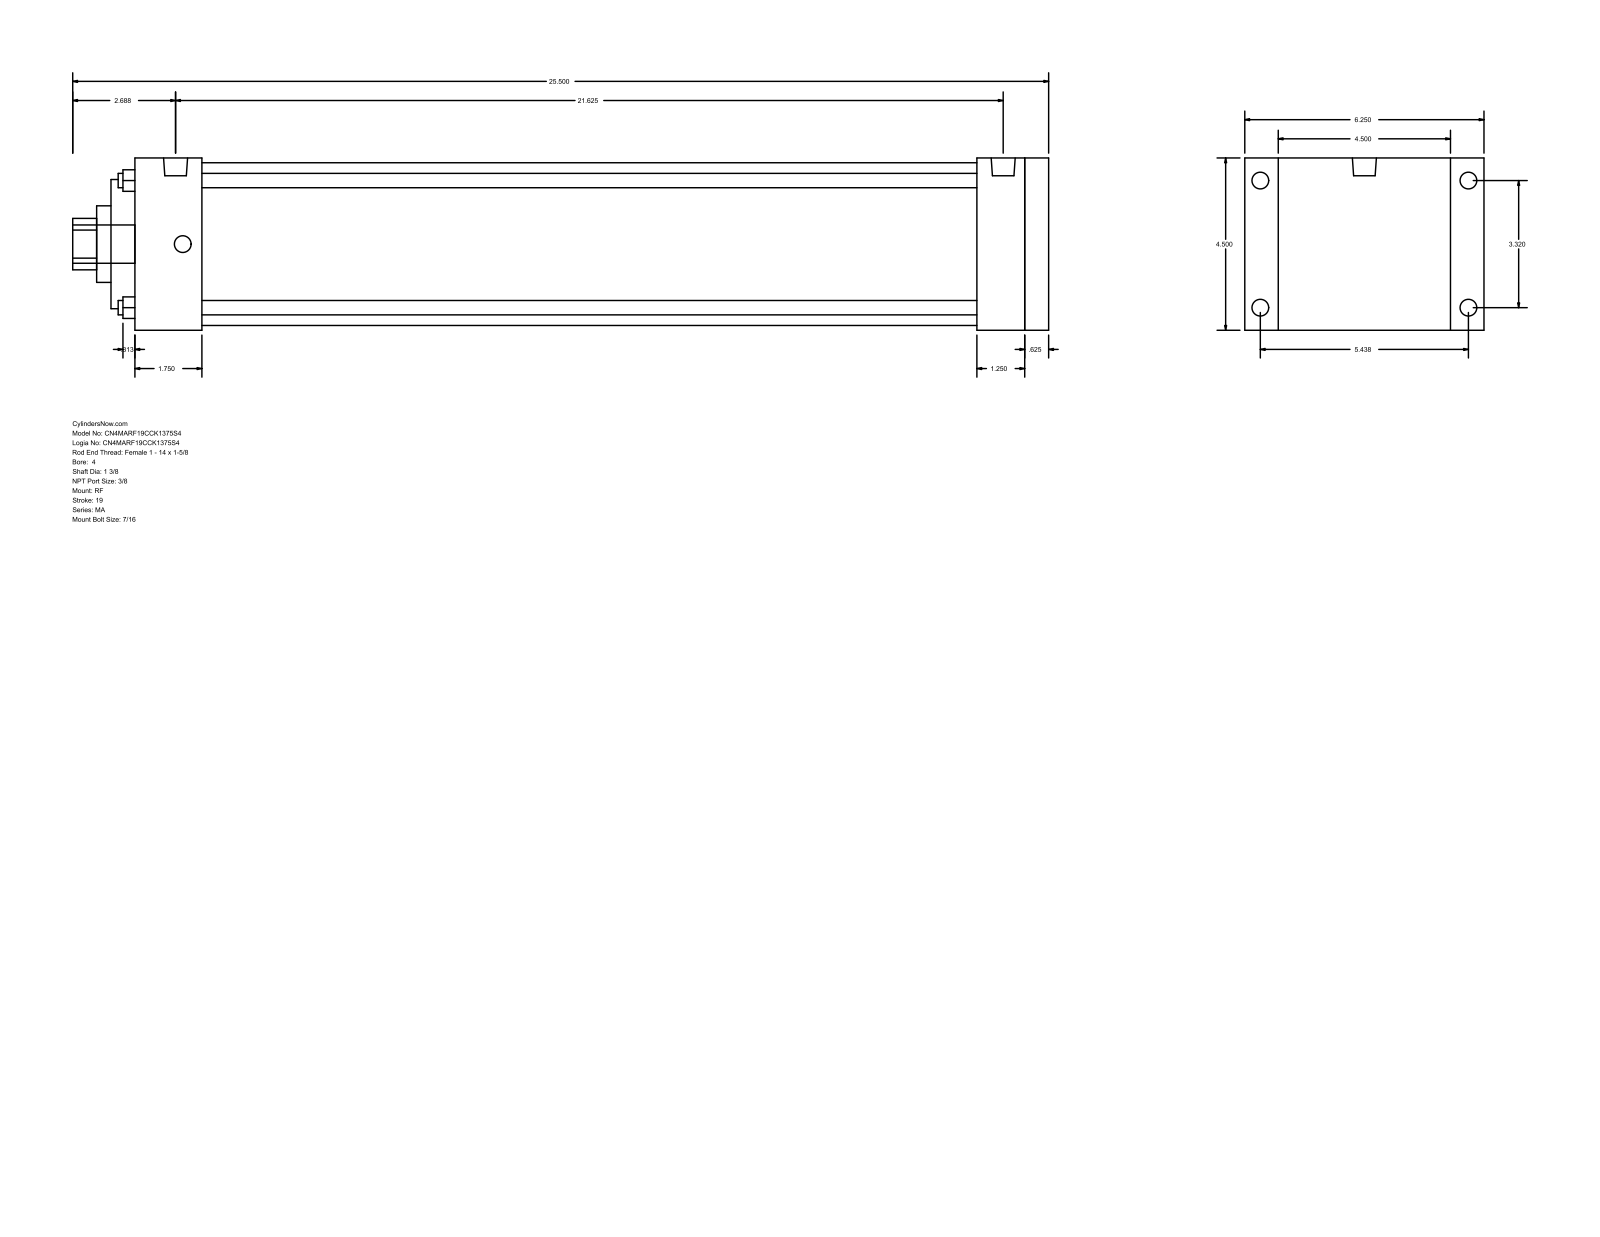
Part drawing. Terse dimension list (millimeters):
name: MA_RF__0400_1.375
written by: GSSL Pune (CONFIG_CONTROL_DESIGN)
unit: mm
bodies: 0 solids, 94 faces (65 planar, 29 cylindrical, 0 other)
size: 647.7 × 158.75 × 114.3
holes: 4× ⌀9.53, 1× ⌀34.92, 1× ⌀50.8, 1× ⌀85.72, 1× ⌀107.95
bosses: 8× ⌀11.11, 2× ⌀15.93, 1× ⌀25.4
rounds: 1× R17.06
face distances: 114.3, 606.43, 15.87, 590.56, 622.3, 22.23, 136.53, 574.68, 558.81, 31.75
hole spacings: 59.62, 84.32, 119.25
